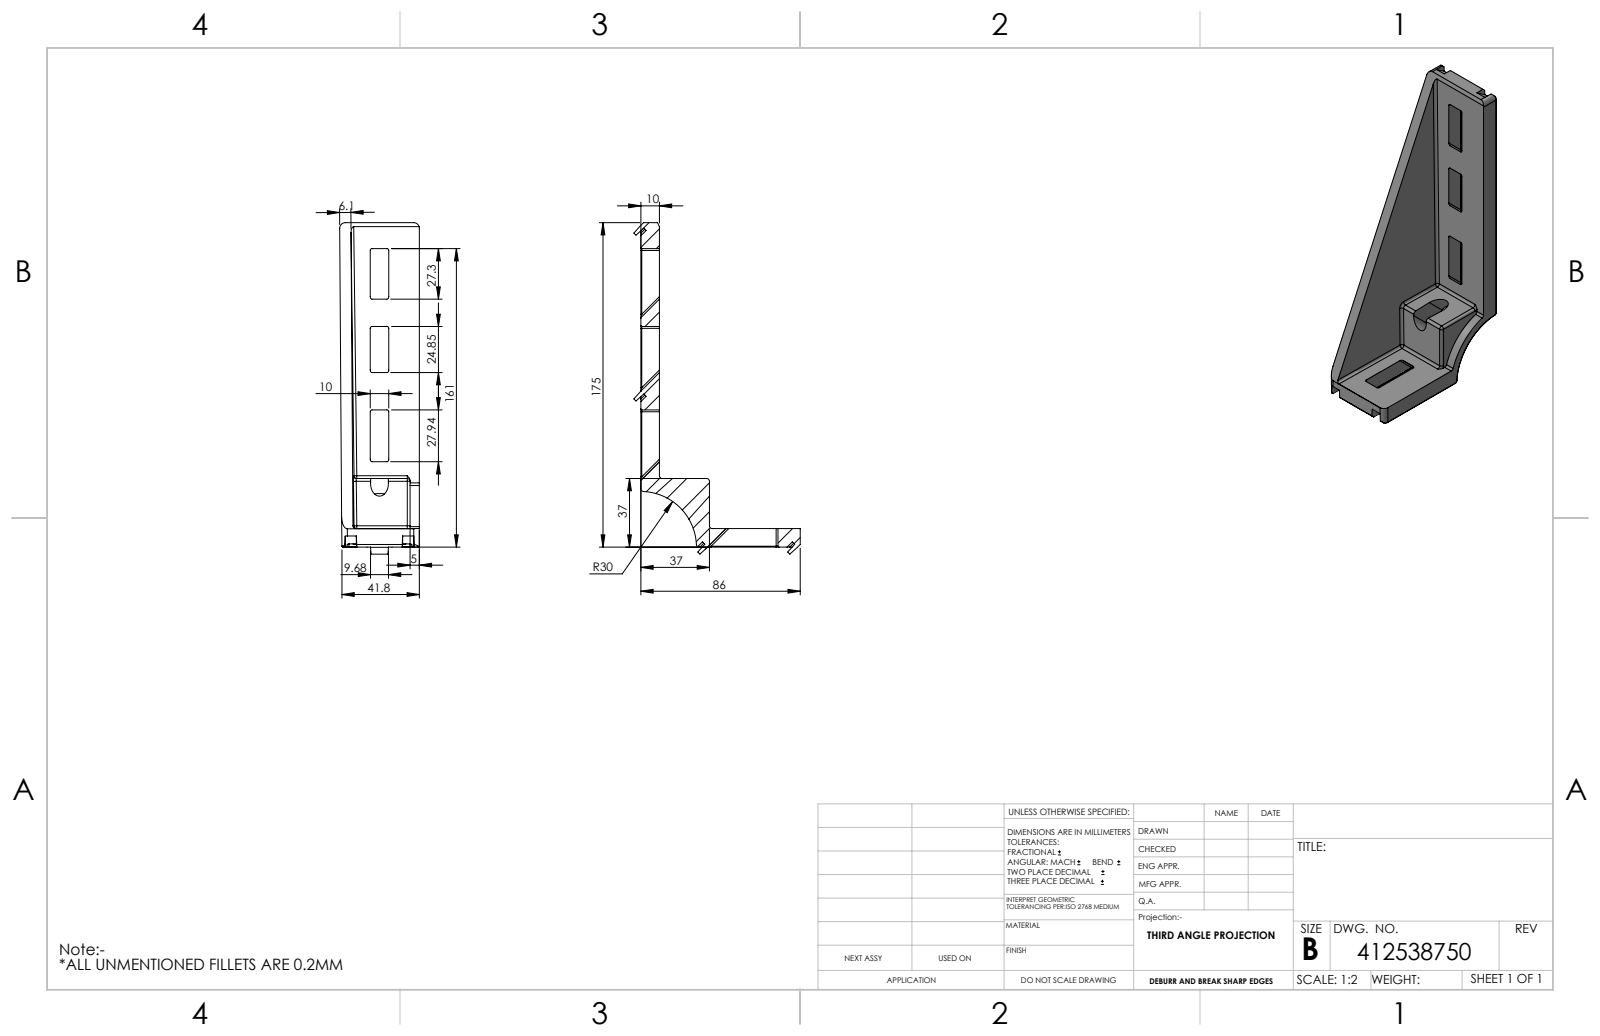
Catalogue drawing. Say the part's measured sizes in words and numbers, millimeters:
The part is named "Syskomp 412523583 Winkel 45x180". Its 3-D file was written by "Autodesk Inventor 2014 (AUTOMOTIVE_DESIGN)". It is 1 solid with 276 faces: 113 planar, 94 cylindrical and 69 other. Overall it measures 178.8 by 89.8 by 42.98 millimeters. Its volume is 105 648 cubic millimeters and its surface area 41 402 square millimeters. Partial cylindrical surfaces (rounded edges, fillets, slot ends): 40 of radius 1, 25 of radius 0.5, 13 of radius 1.5, 4 of radius 3, 1 of radius 30, 1 of radius 35. The main face-to-face distances are 6.15, 5, 10, 25.97, 37, 11.96, 14.01, 32, 27, 14.
